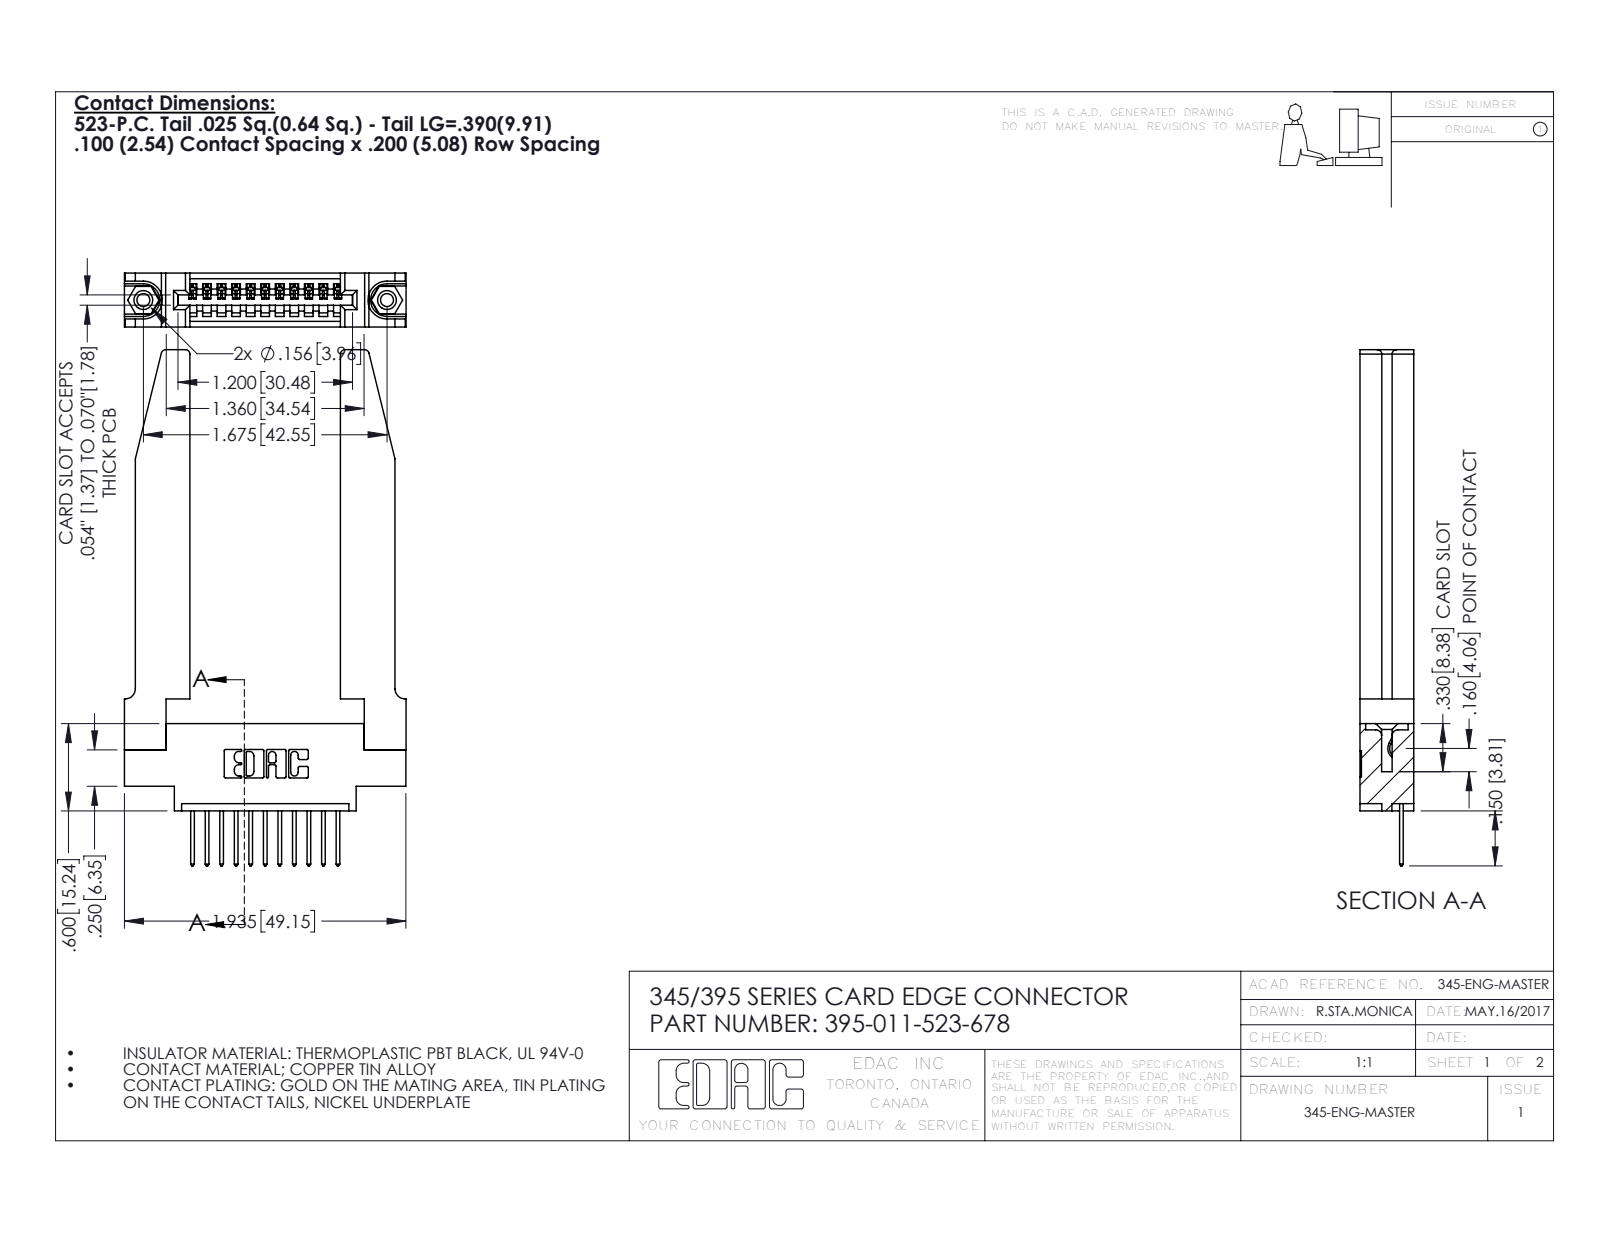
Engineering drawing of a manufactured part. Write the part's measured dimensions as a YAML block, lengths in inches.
part_name: "345-292-001_345-293-123; 395-011-523-678; 345 Part_0.170 Offset - 0.156 Dia-TH; 345-220-078_345-220-078 (+1 more)"
step_written_by: "SolidWorks 2016 (CONFIG_CONTROL_DESIGN)"
units: inches
bodies: {solids: 16, faces: 1002, planar: 666, cylindrical: 284, other: 52}
overall_size: [3.547, 1.936, 0.37]
volume: 0.737
surface_area: 19.03
round_holes:
  - {diameter: 0.089, count: 2}
  - {diameter: 0.125, count: 2}
  - {diameter: 0.156, count: 2}
  - {diameter: 0.064, count: 1}
round_bosses_or_shafts:
  - {diameter: 0.155, count: 2}
partial_cylinders:
  - {radius: 0.006, count: 22}
  - {radius: 0.01, count: 22}
  - {radius: 0.01, count: 22}
  - {radius: 0.03, count: 8}
  - {radius: 0.007, count: 6}
  - {radius: 0.031, count: 6}
  - {radius: 0.026, count: 3}
  - {radius: 0.031, count: 2}
face_to_face_distances: [0.37, 0.072, 0.298, 0.148, 0.15, 0.22, 0.077, 1.035, 0.2, 0.123]
hole_center_spacings: [0.27, 1.443, 1.675]
